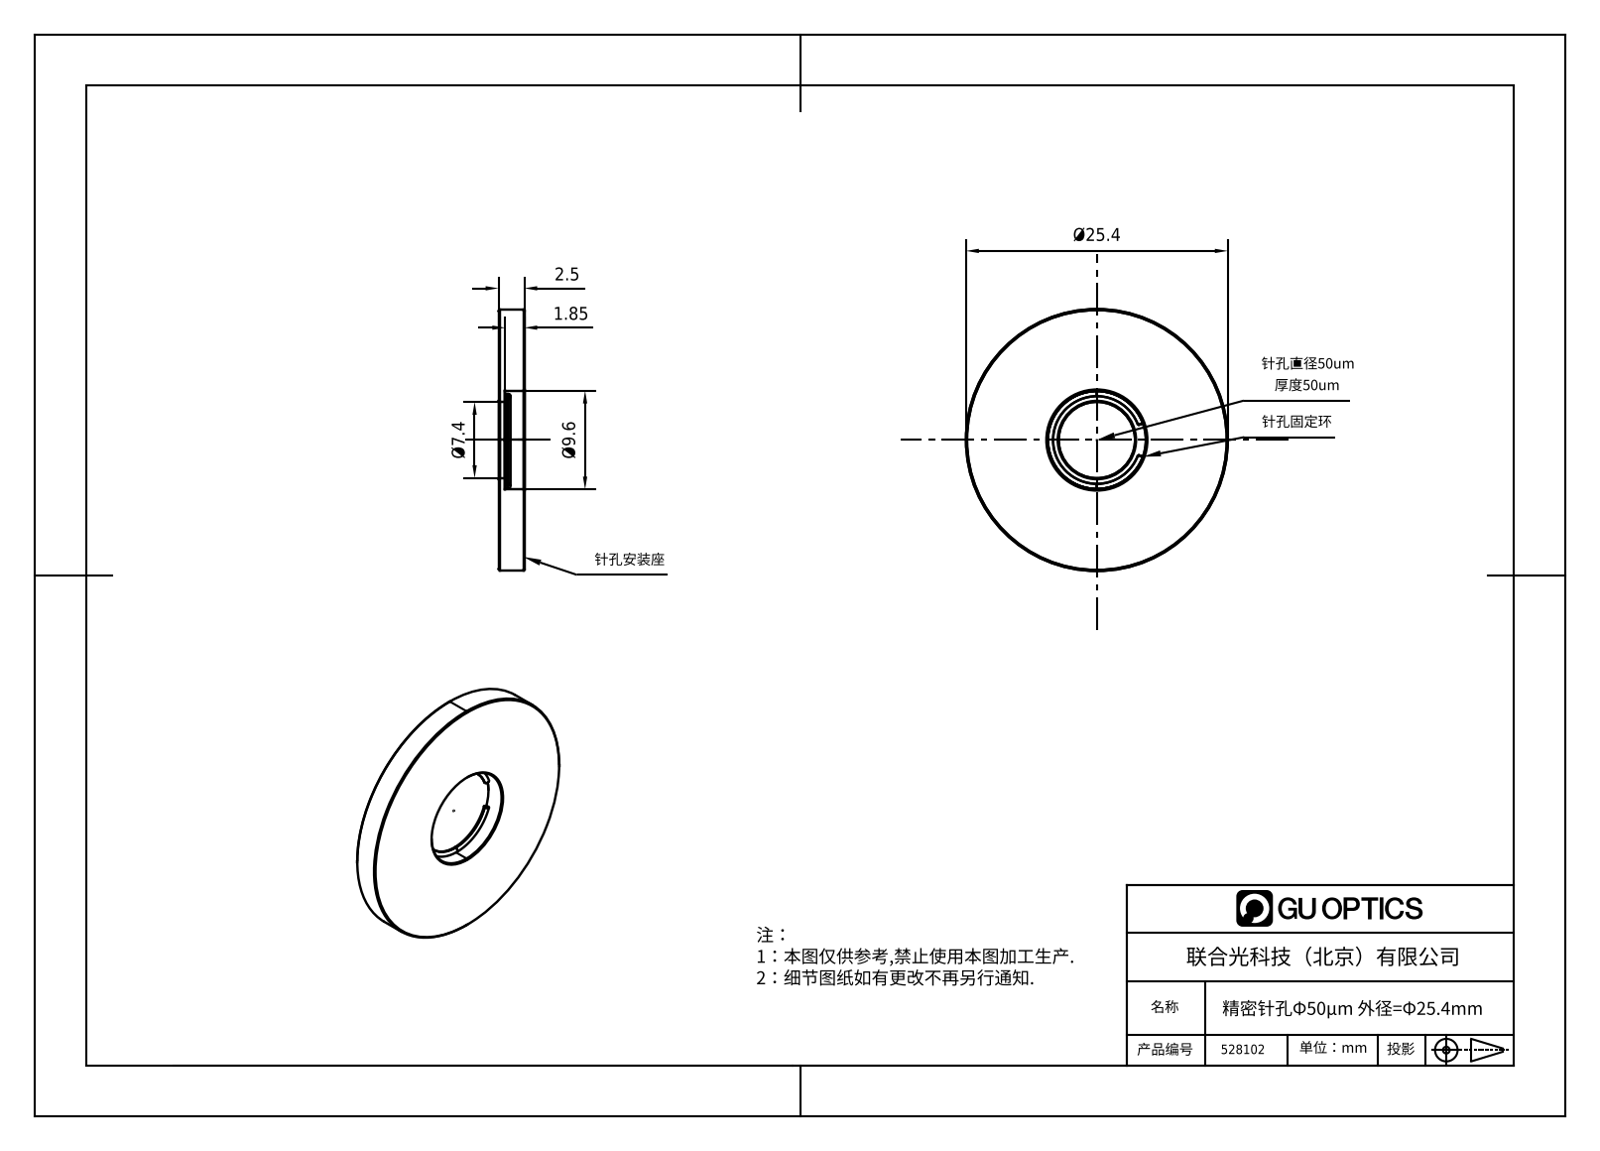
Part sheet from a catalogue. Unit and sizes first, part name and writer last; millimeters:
Units: millimetres
Overall size (bounding box): 25.4 × 25.4 × 2.5
Round holes (diameter × count): ⌀7.4 ×1, ⌀9.6 ×1
Round bosses / shafts (diameter × count): ⌀25.4 ×1
Main face-to-face distances: 2.5, 0.6, 0.65, 1.9, 1.85
Bodies: 0 solids, 26 faces (6 planar, 6 cylindrical, 14 other)
Part name (STEP PRODUCT): 1.5.3.28_ZXO-1.0-50_精密针孔50um，直径25.4（1.0英寸）
STEP written by: SolidWorks 2018 (CONFIG_CONTROL_DESIGN)
